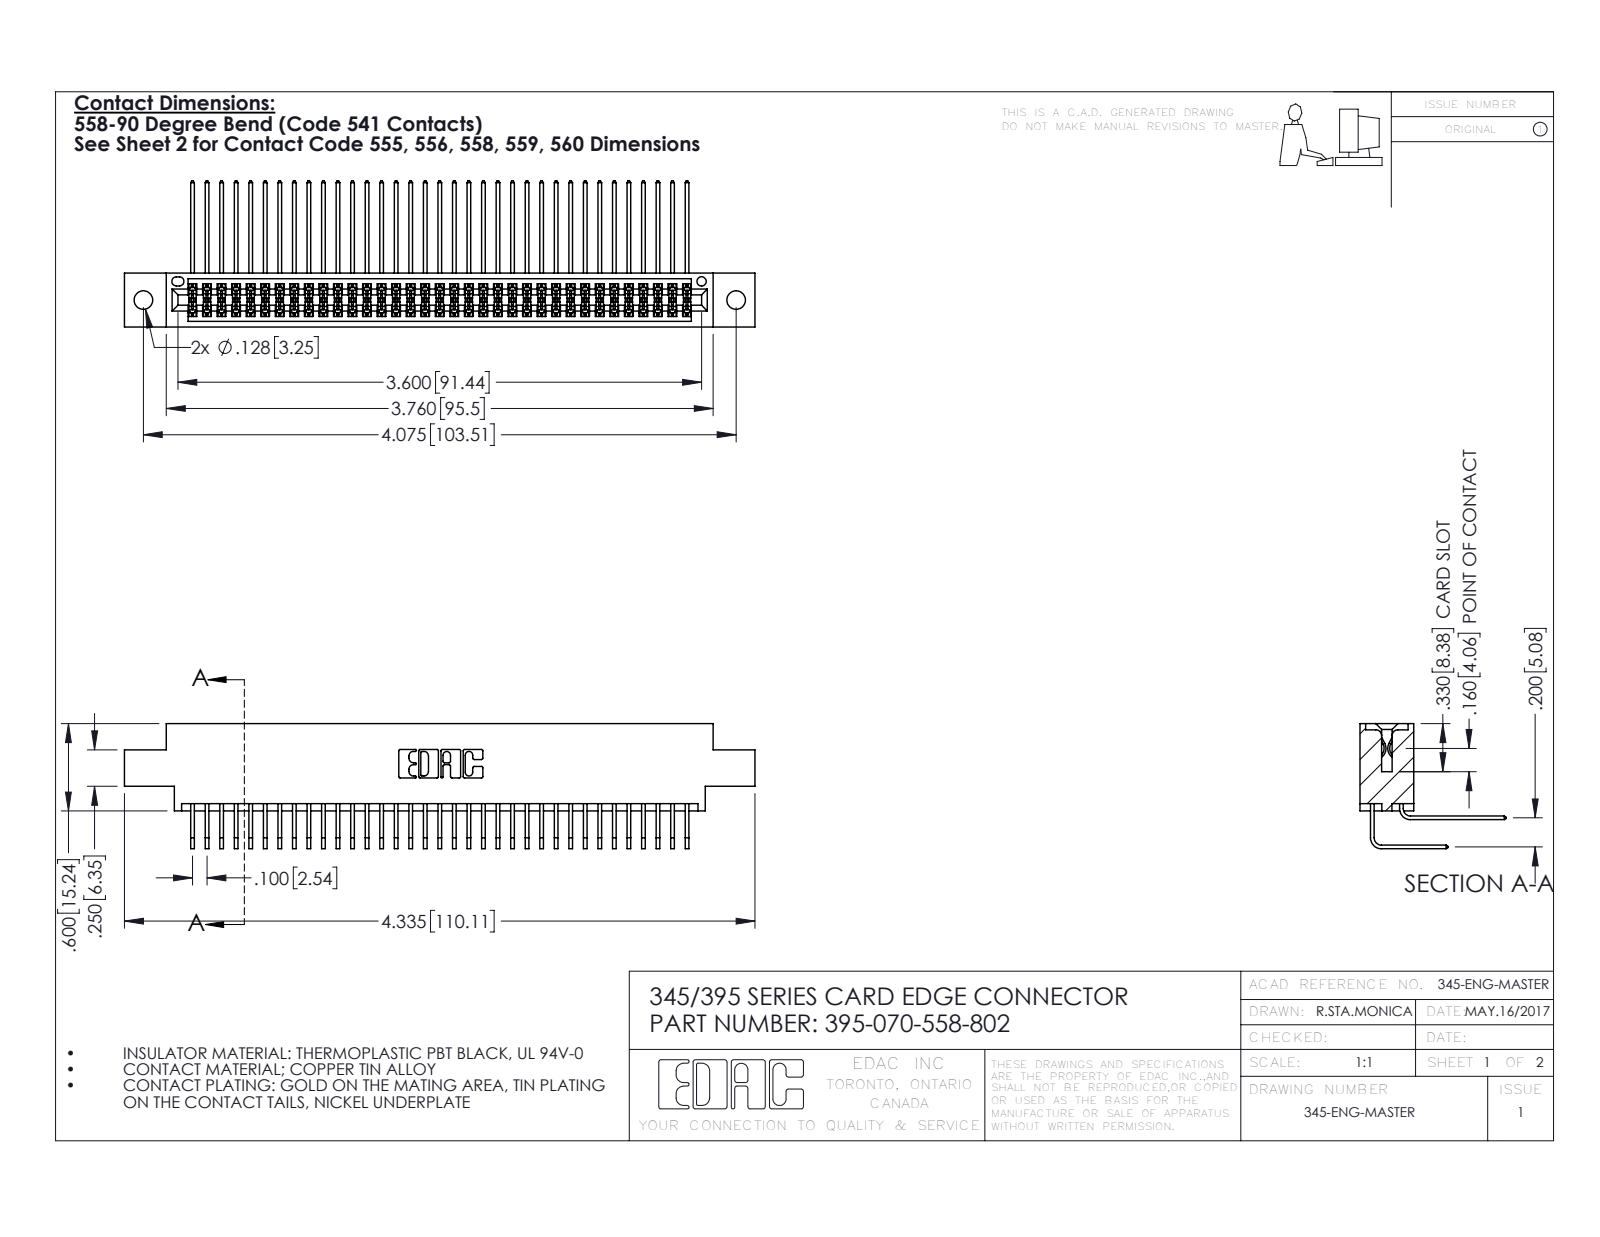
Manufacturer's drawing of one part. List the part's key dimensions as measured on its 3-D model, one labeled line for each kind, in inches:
Part name (STEP PRODUCT): 395-070-558-802; 345 Part_0.170 Offset - 0.128 Dia; 345-292-001_558 Tail - 2; 345-292-001_558 559 Tail - 1
STEP written by: SolidWorks 2016 (CONFIG_CONTROL_DESIGN)
Units: inches
Bodies: 71 solids, 3770 faces (2534 planar, 1236 cylindrical, 0 other)
Overall size (bounding box): 4.335 × 1.005 × 0.859
Volume: 0.664 in³ · Surface area: 27.47 in²
Round holes (diameter × count): ⌀0.128 ×2, ⌀0.064 ×1
Partial cylindrical surfaces — rounded edges, fillets, slot ends (radius × count): R0.006 ×106, R0.01 ×22, R0.007 ×6, R0.031 ×6, R0.026 ×3, R0.014 ×2, R0.019 ×2, R0.022 ×2
Main face-to-face distances: 0.072, 0.298, 0.2, 0.37, 0.098, 0.272, 0.025, 0.225, 0.175, 0.025
Hole centre spacings: 0.27, 3.839, 4.075
